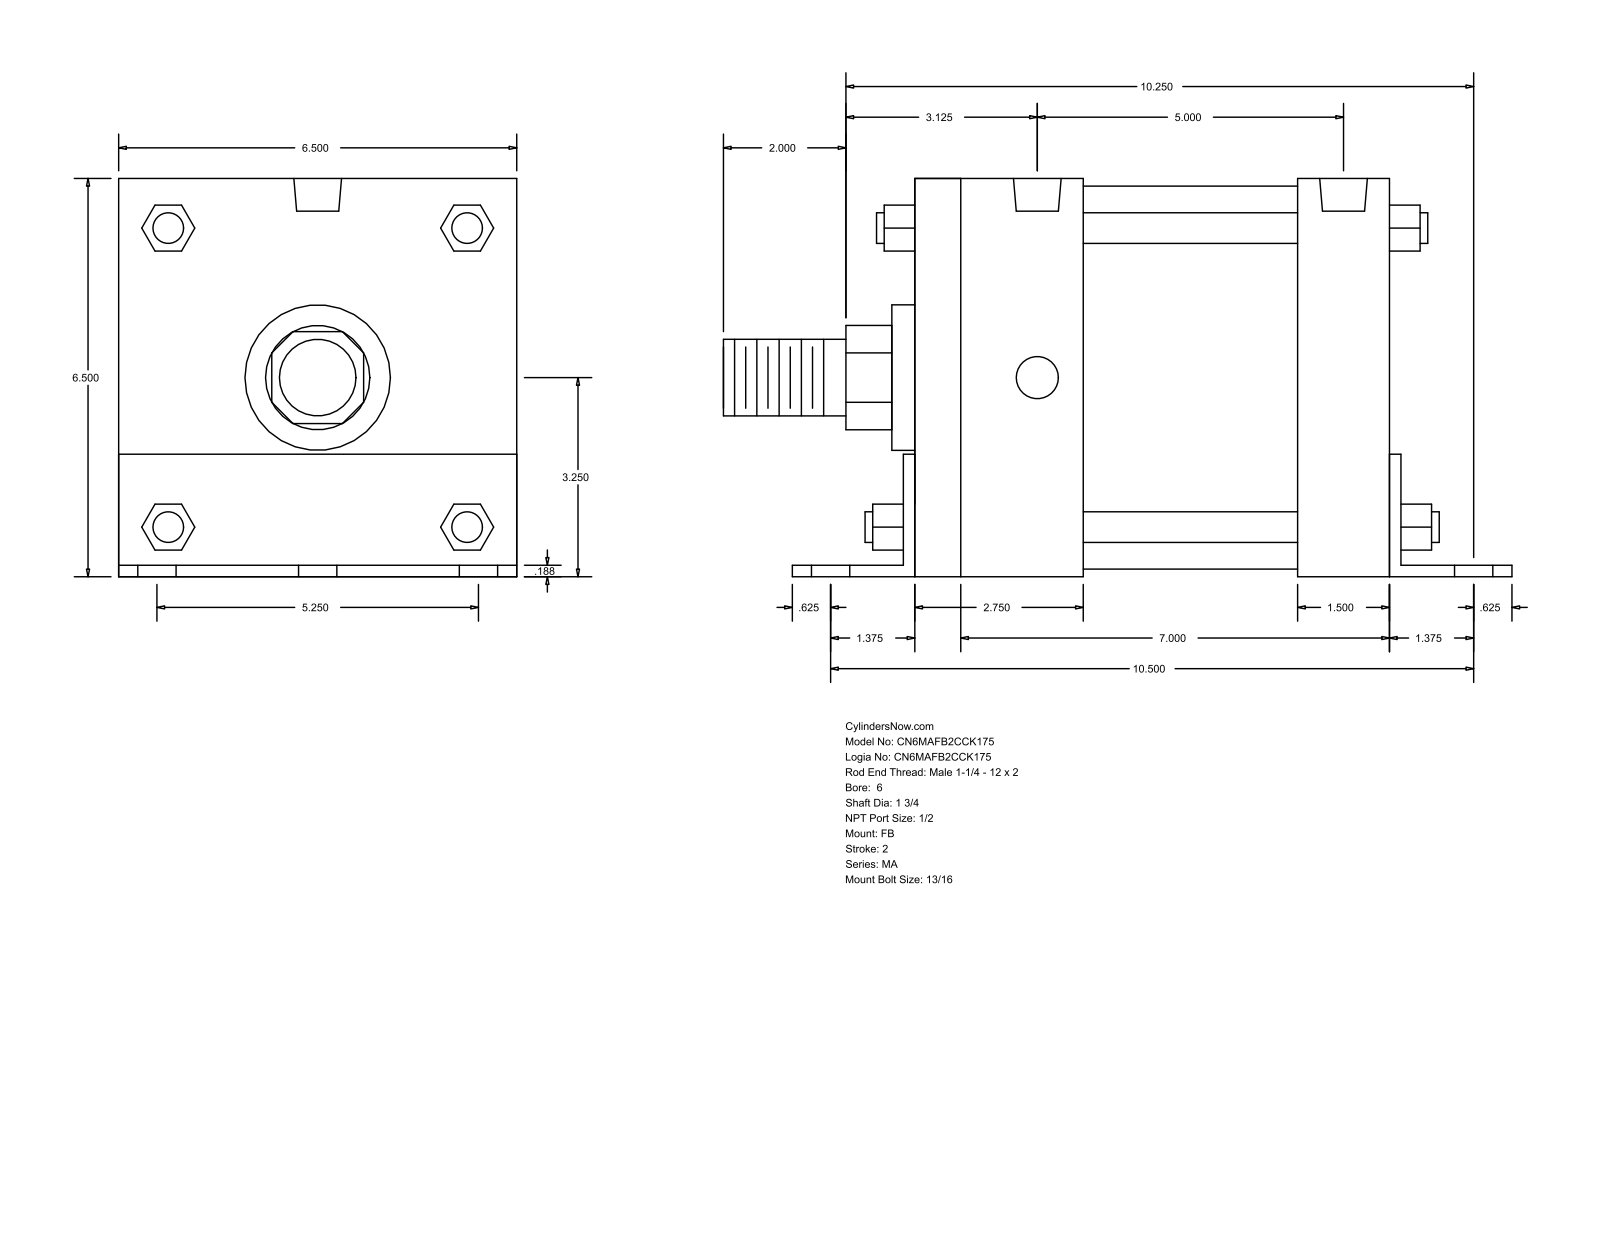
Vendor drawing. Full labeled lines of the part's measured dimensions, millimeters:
Part name (STEP PRODUCT): MA_FB__0600_1.75
STEP written by: GSSL Pune (CONFIG_CONTROL_DESIGN)
Units: millimetres
Bodies: 0 solids, 140 faces (105 planar, 35 cylindrical, 0 other)
Overall size (bounding box): 327.02 × 165.15 × 165.1
Round holes (diameter × count): ⌀20.64 ×6, ⌀17.46 ×4, ⌀19.77 ×2
Round bosses / shafts (diameter × count): ⌀12.7 ×4, ⌀158.75 ×1, ⌀60.33 ×1, ⌀44.45 ×1, ⌀31.75 ×1
Partial cylindrical surfaces — rounded edges, fillets, slot ends (radius × count): R21.63 ×1, R32.05 ×1
Main face-to-face distances: 165.1, 4.76, 196.86, 165.15, 201.62, 4.71, 160.39, 206.38, 38.11, 69.85
Hole centre spacings: 66.67, 274.91, 266.7, 85.78, 108.6, 127, 133.34, 192.86
